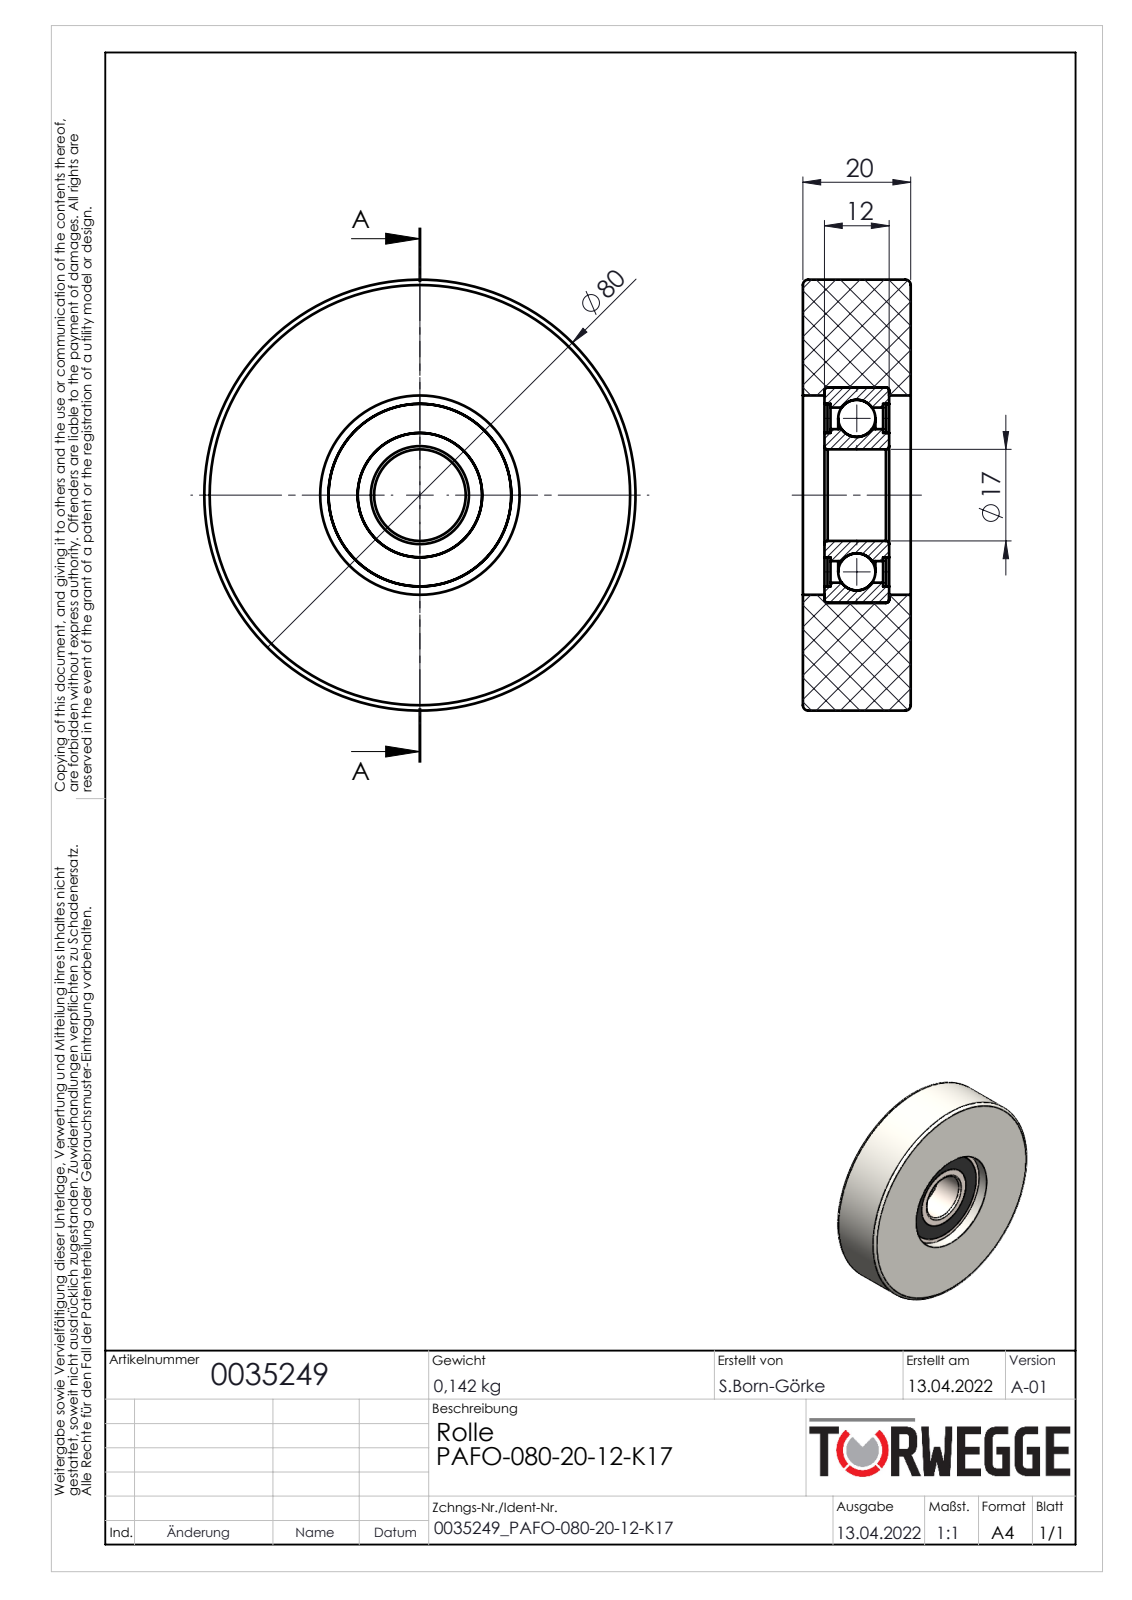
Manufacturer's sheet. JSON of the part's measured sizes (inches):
{"part_name": "0035249", "step_written_by": "SolidWorks 2020 (AUTOMOTIVE_DESIGN)", "units": "inches", "bodies": {"solids": 6, "faces": 78, "planar": 16, "cylindrical": 36, "other": 26}, "overall_size": [3.15, 3.15, 0.787], "volume_in3": 5.332, "surface_area_in2": 39.13, "round_holes": [[0.669, 1], [0.909, 1], [1.28, 1], [1.335, 1], [1.457, 1], [1.575, 1]], "round_bosses_or_shafts": [[3.15, 1], [0.965, 1]], "face_to_face_distances": [0.787, 0.157, 0.63, 0.022, 0.472, 0.18, 0.608, 0.45, 0.428, 0.202]}
